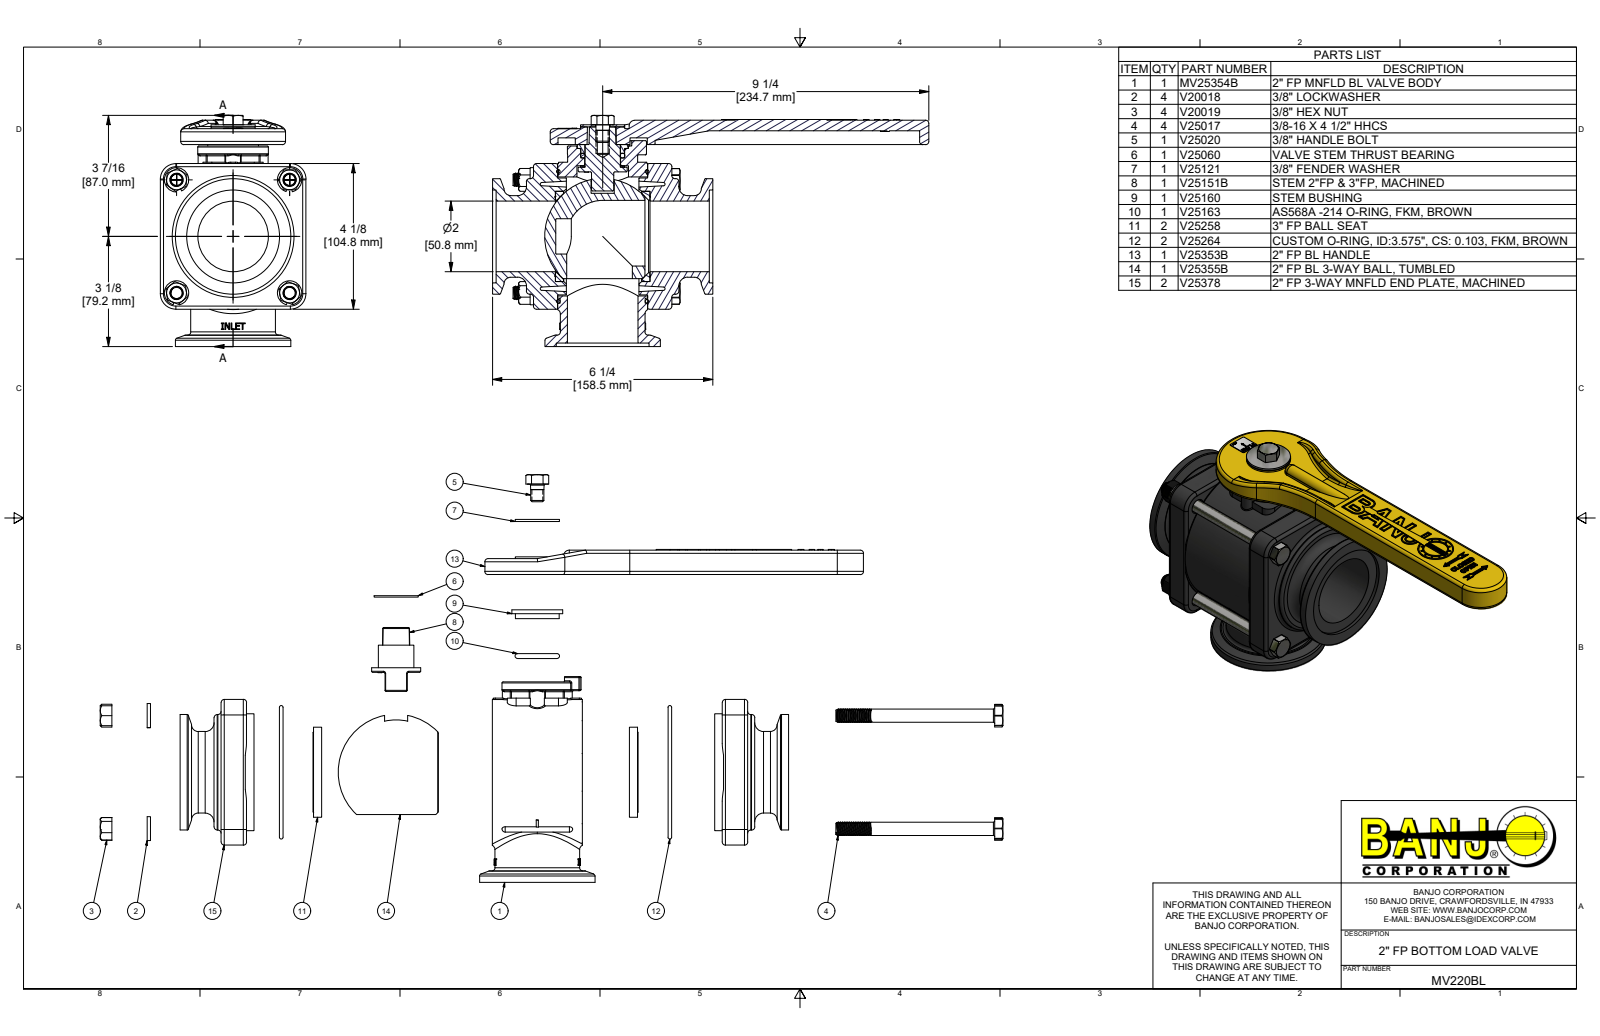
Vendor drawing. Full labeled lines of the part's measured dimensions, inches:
Part name (STEP PRODUCT): MV220BL; MV25354B; V25378; V25378X (+8 more)
STEP written by: Autodesk Inventor 2022 (AUTOMOTIVE_DESIGN)
Units: inches
Bodies: 28 solids, 1916 faces (824 planar, 485 cylindrical, 607 other)
Overall size (bounding box): 12.36 × 6.545 × 4.125
Volume: 58.56 in³ · Surface area: 451.2 in²
Round holes (diameter × count): ⌀0.17 ×12, ⌀0.307 ×4, ⌀0.385 ×4, ⌀0.438 ×4, ⌀1 ×2, ⌀2 ×2, ⌀2.04 ×2, ⌀2.63 ×2, ⌀0.307 ×1, ⌀0.406 ×1, ⌀0.681 ×1, ⌀0.962 ×1
Round bosses / shafts (diameter × count): ⌀0.324 ×60, ⌀0.375 ×5, ⌀0.687 ×4, ⌀3.27 ×2, ⌀4.125 ×1, ⌀3.5 ×1, ⌀3.31 ×1, ⌀2.969 ×1
Partial cylindrical surfaces — rounded edges, fillets, slot ends (radius × count): R0.09 ×26, R0.03 ×18, R0.032 ×10, R0.062 ×8, R0.162 ×8, R0.25 ×5, R0.031 ×4, R0.06 ×4
Main face-to-face distances: 0.685, 3.235, 0.1, 1.78, 2.55, 4.36, 4.125, 0.62, 3.3, 0.065
Hole centre spacings: 1.977, 2.796, 3.82, 1.023, 1.133, 2.136, 3.007, 3.424
